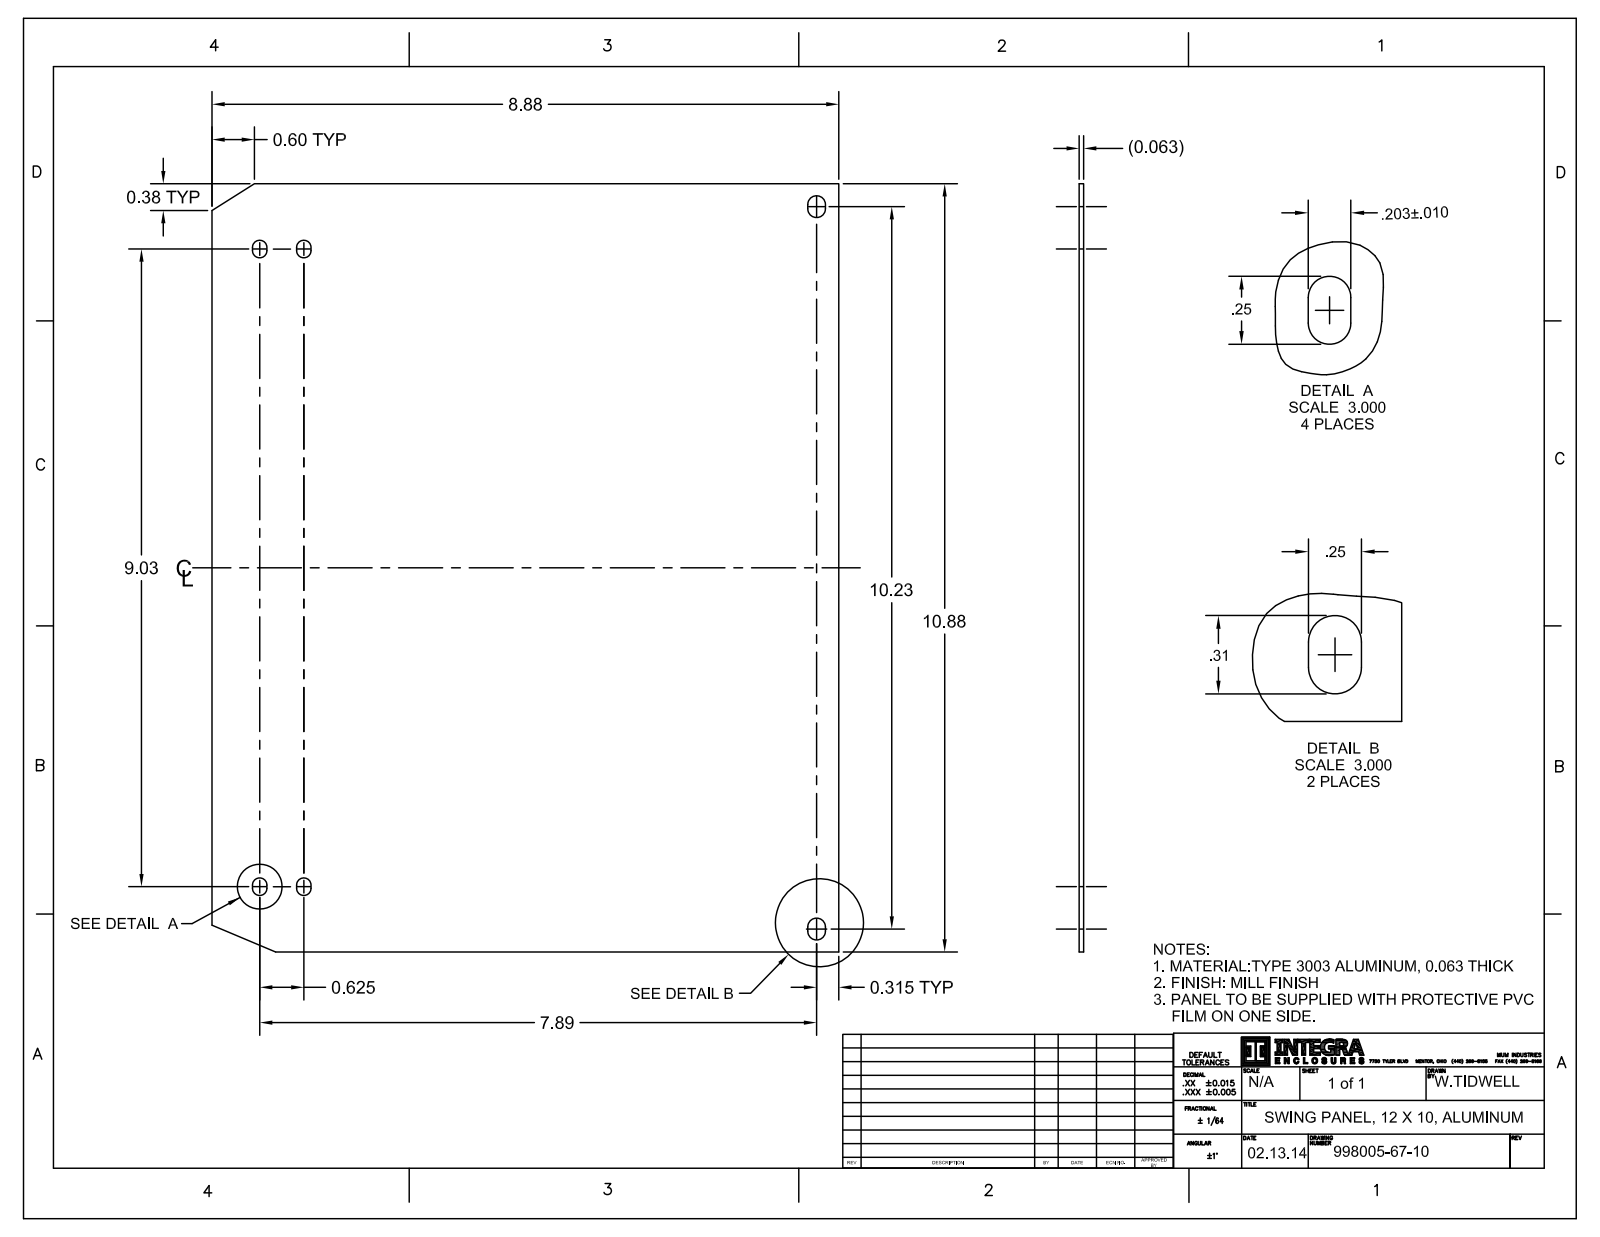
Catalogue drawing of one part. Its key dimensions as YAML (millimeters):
part_name: "9912511-20-50; 9912525-80-10; 9912511-20-50_ASM; 995008-20-90 (+8 more)"
step_written_by: "CREO PARAMETRIC BY PTC INC, 2016050 (CONFIG_CONTROL_DESIGN)"
units: millimeters
bodies: {solids: 31, faces: 2116, planar: 478, cylindrical: 994, other: 644}
overall_size: [297.5, 246.7, 41.2]
volume: 168100
surface_area: 158600
round_holes:
  - {diameter: 4.8, count: 8}
  - {diameter: 6.2, count: 8}
  - {diameter: 9.1, count: 8}
  - {diameter: 5.3, count: 4}
  - {diameter: 8, count: 4}
  - {diameter: 6.9, count: 2}
round_bosses_or_shafts:
  - {diameter: 6.4, count: 12}
  - {diameter: 7.6, count: 8}
  - {diameter: 7.6, count: 8}
  - {diameter: 7.4, count: 8}
  - {diameter: 6.6, count: 8}
  - {diameter: 6.6, count: 8}
  - {diameter: 11.2, count: 6}
  - {diameter: 10.9, count: 6}
partial_cylinders:
  - {radius: 0.8, count: 124}
  - {radius: 0.1, count: 48}
  - {radius: 0.1, count: 42}
  - {radius: 1.3, count: 36}
  - {radius: 0.7, count: 16}
  - {radius: 1.2, count: 16}
  - {radius: 1.5, count: 16}
  - {radius: 0.5, count: 12}
face_to_face_distances: [1.9, 12.7, 2.1, 9.7, 230.3, 16.7, 29.4, 247, 259.7, 2.8]
hole_center_spacings: [15.9, 17.2, 28.7, 36, 185.2, 201.1, 209.2, 230.3]
